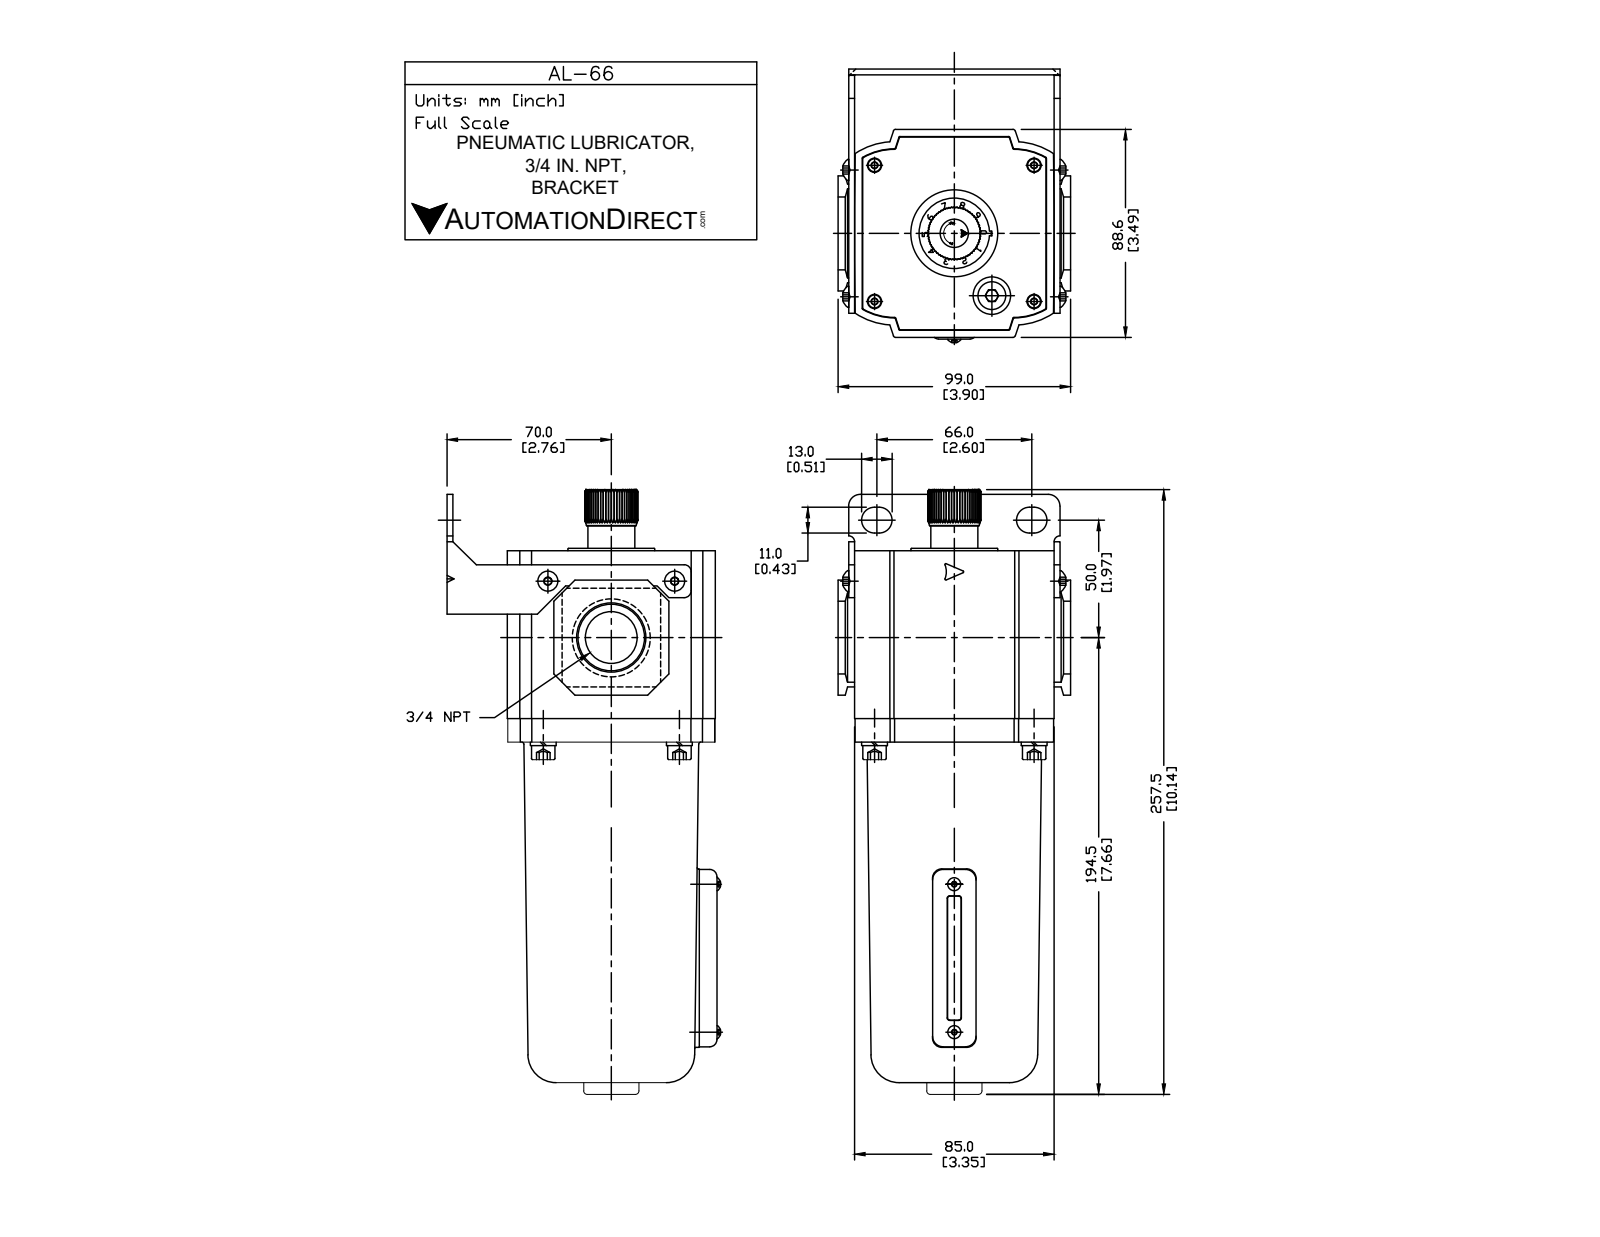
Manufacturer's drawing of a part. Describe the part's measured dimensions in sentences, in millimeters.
The part is named "AL-66". Its 3-D file was written by "SolidWorks 2015 (CONFIG_CONTROL_DESIGN)". It is 6 solids with 570 faces: 343 planar, 109 cylindrical and 118 other. Overall it measures 257.5 by 116.49 by 99 millimeters. Its volume is 1 249 000 cubic millimeters and its surface area 114 125 square millimeters. Round holes: 2 of diameter 5.5, 1 of diameter 23.01. Round bosses or shafts: 4 of diameter 10, 1 of diameter 74.5, 1 of diameter 60, 1 of diameter 23.5, 1 of diameter 20. Partial cylindrical surfaces (rounded edges, fillets, slot ends): 10 of radius 3, 5 of radius 2, 4 of radius 0.3, 4 of radius 1, 4 of radius 5.5, 4 of radius 29.7, 4 of radius 30, 3 of radius 0.2. The main face-to-face distances are 2.5, 71.5, 7, 87.5, 92, 25.7, 23.2, 114.3, 111.8, 88.6. The hole center spacings are 36.12, 54.
